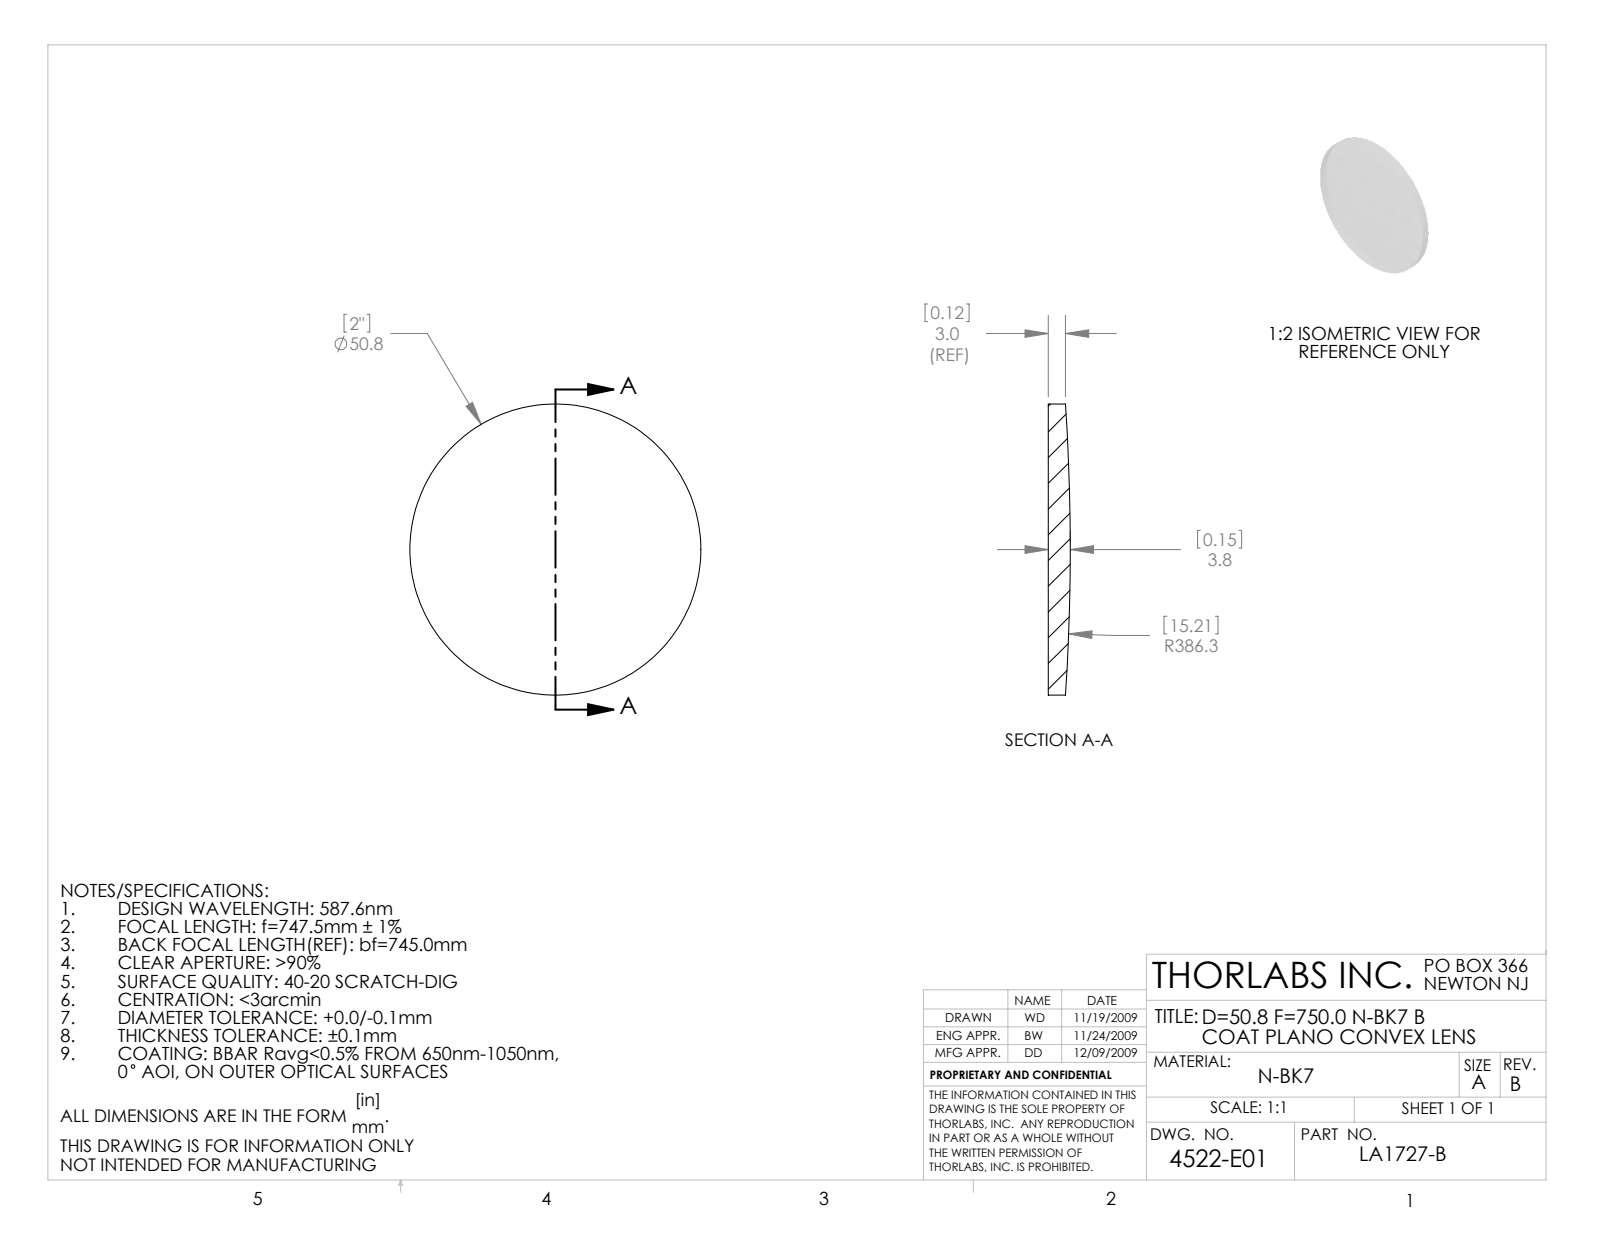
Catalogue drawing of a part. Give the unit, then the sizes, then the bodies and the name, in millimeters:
Units: millimetres
Overall size (bounding box): 50.8 × 50.8 × 3.83
Round bosses / shafts (diameter × count): ⌀50.8 ×1
Volume: 6 916 mm³ · Surface area: 4 534 mm²
Bodies: 1 solid, 5 faces (1 planar, 2 cylindrical, 2 other)
Part name (STEP PRODUCT): 4522-E0W
STEP written by: SolidWorks 2009 (AUTOMOTIVE_DESIGN)
